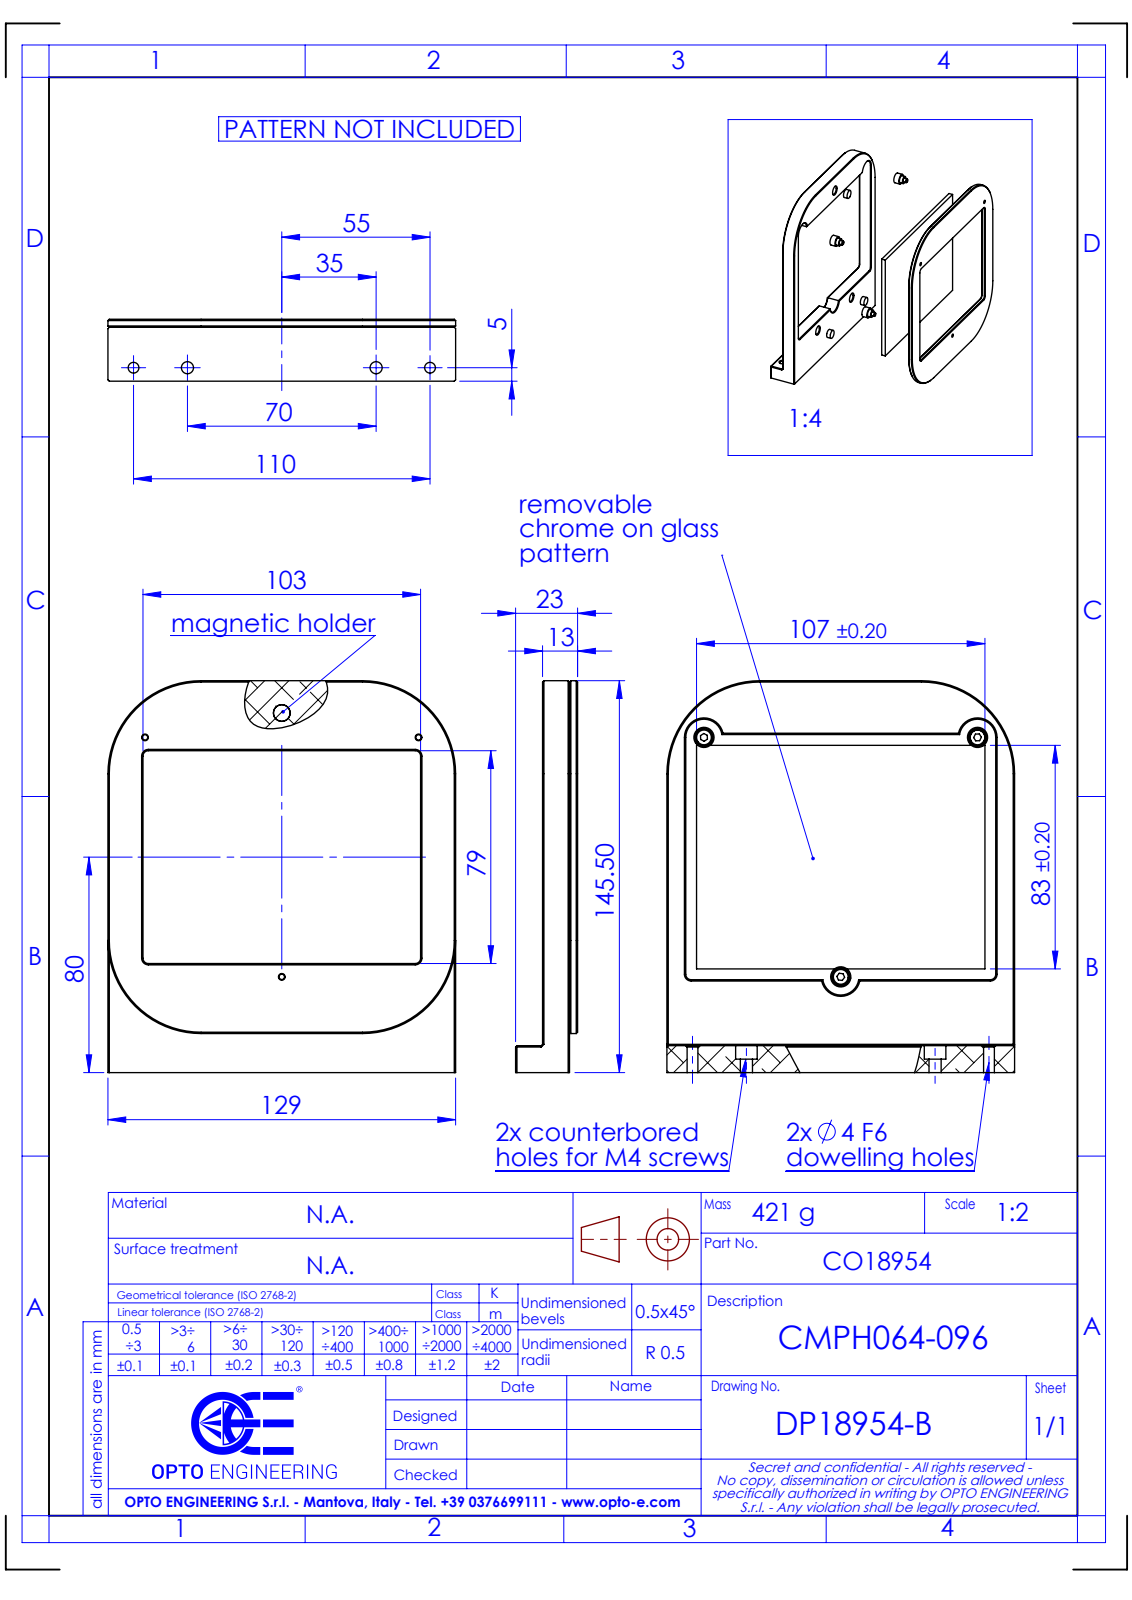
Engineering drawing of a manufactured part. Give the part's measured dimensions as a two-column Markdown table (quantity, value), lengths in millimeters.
| quantity | value |
| --- | --- |
| part name | DP18954-B_CMPH064-096 |
| STEP written by | SolidWorks 2021 (CONFIG_CONTROL_DESIGN) |
| units | millimeters |
| bodies | 0 solids, 186 faces (89 planar, 51 cylindrical, 46 other) |
| overall size | 145.5 × 129 × 23 |
| round holes (diameter × count) | 2.5 × 3, 4 × 2, 4.5 × 2, 8 × 2 |
| round bosses / shafts (diameter × count) | 7.5 × 3, 5.5 × 3 |
| partial cylindrical surfaces (radius × count) | 2 × 6, 34.56 × 4, 6.75 × 3 |
| main face-to-face distances | 10, 3, 13, 20, 7, 122, 129, 23, 34.5, 24.5 |
| hole center spacings | 20, 90, 102.37, 70, 101.5, 110 |
